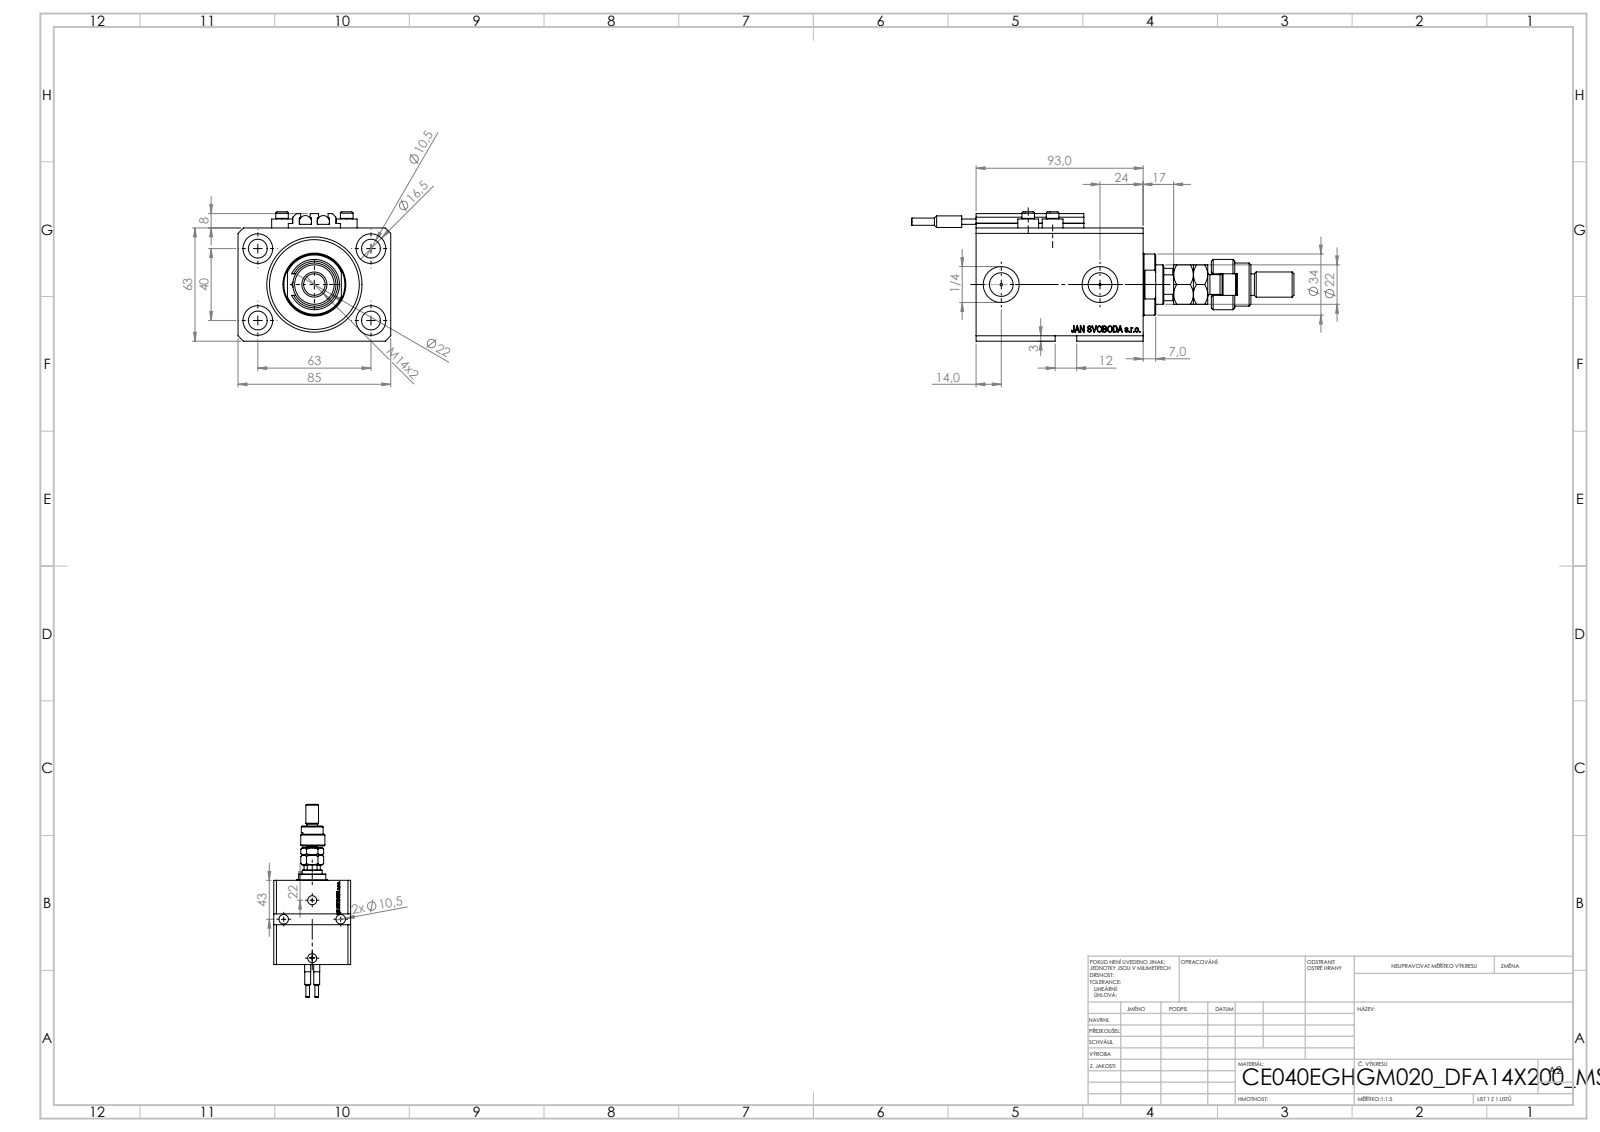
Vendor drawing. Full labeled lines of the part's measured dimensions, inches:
Part name (STEP PRODUCT): V250CE_C_VCP; V250CE_E_Body; SWITCH_V250CE; MFA (+3 more)
STEP written by: SolidWorks 2019 (CONFIG_CONTROL_DESIGN)
Units: inches
Bodies: 12 solids, 1224 faces (595 planar, 151 cylindrical, 478 other)
Overall size (bounding box): 8.382 × 3.346 × 2.835
Volume: 28.24 in³ · Surface area: 168.4 in²
Round holes (diameter × count): ⌀0.413 ×6, ⌀0.049 ×4, ⌀0.157 ×4, ⌀0.65 ×4, ⌀0.394 ×2, ⌀0.518 ×2, ⌀0.787 ×2, ⌀0.492 ×1, ⌀0.866 ×1, ⌀1.575 ×1, ⌀2.087 ×1
Round bosses / shafts (diameter × count): ⌀0.457 ×4, ⌀0.276 ×4, ⌀0.268 ×2, ⌀0.256 ×2, ⌀0.157 ×2, ⌀1.339 ×1, ⌀1.102 ×1, ⌀0.945 ×1
Partial cylindrical surfaces — rounded edges, fillets, slot ends (radius × count): R0.008 ×10, R0.384 ×1, R0.413 ×1
Main face-to-face distances: 2.48, 3.346, 3.661, 2.594, 2.146, 1.067, 0.118, 0.449, 3.213, 2.559
Hole centre spacings: 1.469, 2.48, 0.535, 0.606, 0.983, 1.103, 1.119, 1.324
